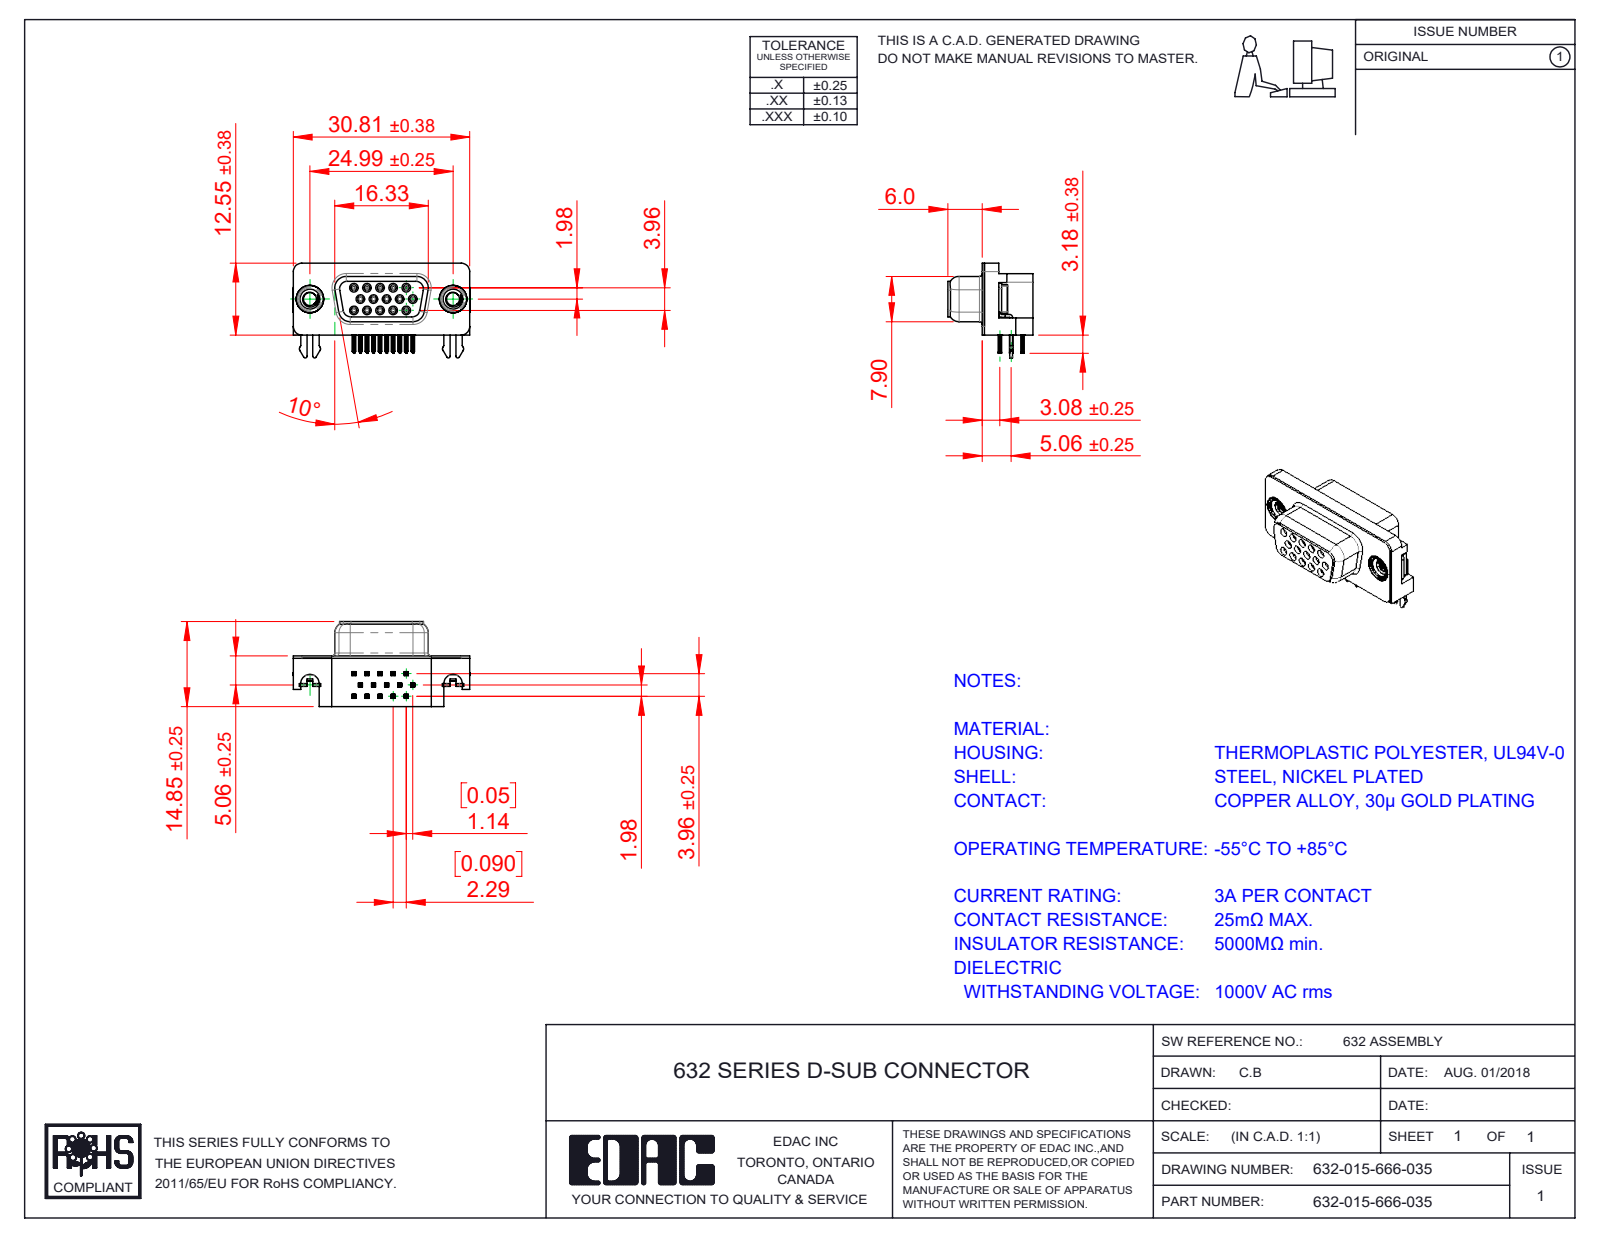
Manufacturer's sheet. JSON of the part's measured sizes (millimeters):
{"part_name": "632 Contact Bottom; 632-015-666-035; 632 Shell_9 Socket; 632 Contact Middle (+5 more)", "step_written_by": "SolidWorks 2016 (CONFIG_CONTROL_DESIGN)", "units": "millimeters", "bodies": {"solids": 23, "faces": 2426, "planar": 1006, "cylindrical": 654, "other": 766}, "overall_size": [30.89, 16.55, 14.85], "volume_mm3": 2996, "surface_area_mm2": 5342, "round_holes": [[0.8, 15], [0.9, 15], [2.26, 2], [2.5, 2], [4, 2], [4.8, 2], [5, 2]], "round_bosses_or_shafts": [[1.2, 15], [4.9, 2], [4.75, 2], [3.9, 2]], "partial_cylinders_radius": [[0.1, 120], [0.15, 60], [0.35, 30], [0.34, 15], [1, 11], [0.28, 10], [0.5, 10], [0.25, 8]], "face_to_face_distances": [0.4, 8.45, 8.85, 1.98, 2.9, 5.95, 2.5, 6.4, 6.7, 7.05], "hole_center_spacings": [2.28, 2.29, 3.96, 4.57, 6.05, 3.97, 4.58, 6.86]}
